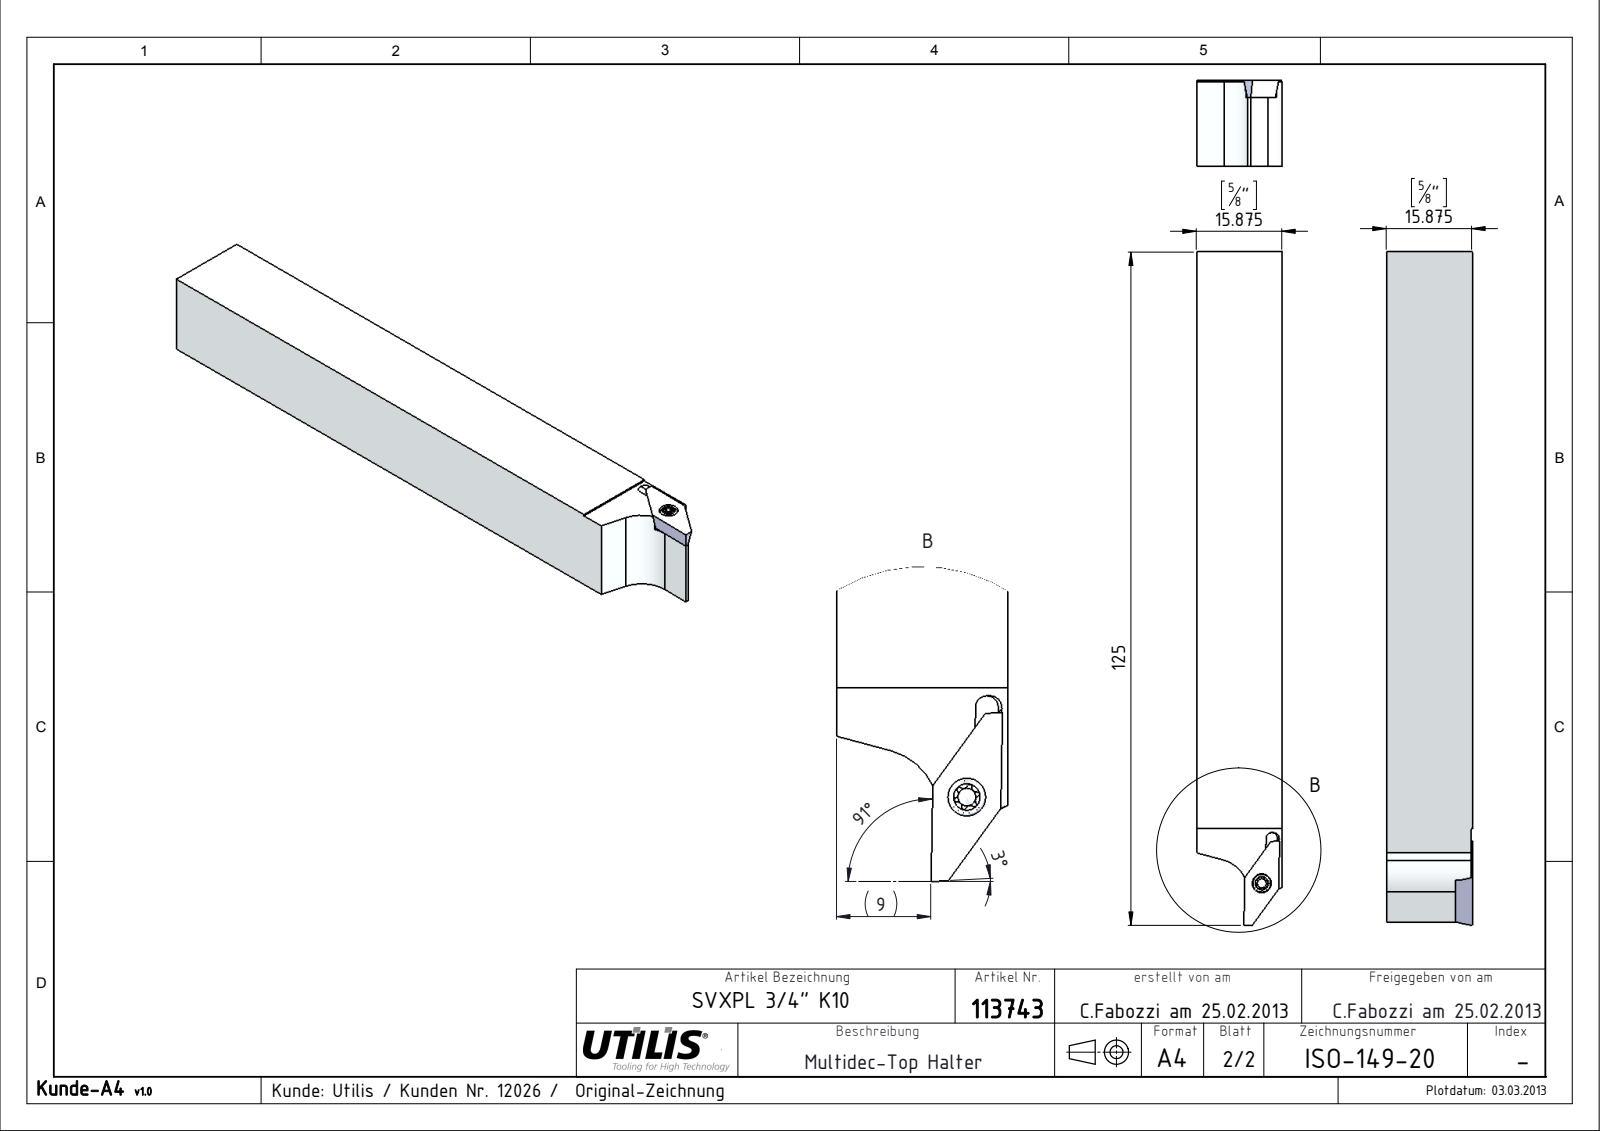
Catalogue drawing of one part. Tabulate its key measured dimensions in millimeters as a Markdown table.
| quantity | value |
| --- | --- |
| part name | ISO-149-Kunde_20; VPGT 10 L_01; MSP-7_M2,5X6-TX8 CERATIZIT Schraube; ISO-149-20 |
| STEP written by | SolidWorks 2015 (CONFIG_CONTROL_DESIGN) |
| units | millimeters |
| bodies | 3 solids, 72 faces (28 planar, 27 cylindrical, 17 other) |
| overall size | 125 × 19.05 × 19.05 |
| volume | 41 821 mm³ |
| surface area | 10 124 mm² |
| round holes (diameter × count) | 2.05 × 1, 3 × 1 |
| round bosses / shafts (diameter × count) | 3.45 × 1, 2.5 × 1 |
| partial cylindrical surfaces (radius × count) | 0.2 × 6, 0.45 × 6, 6 × 2, 1.05 × 1 |
| main face-to-face distances | 19.05, 18.75, 15.87, 2.88, 3.18, 5.33, 2.1, 3.23, 5.32, 107 |
